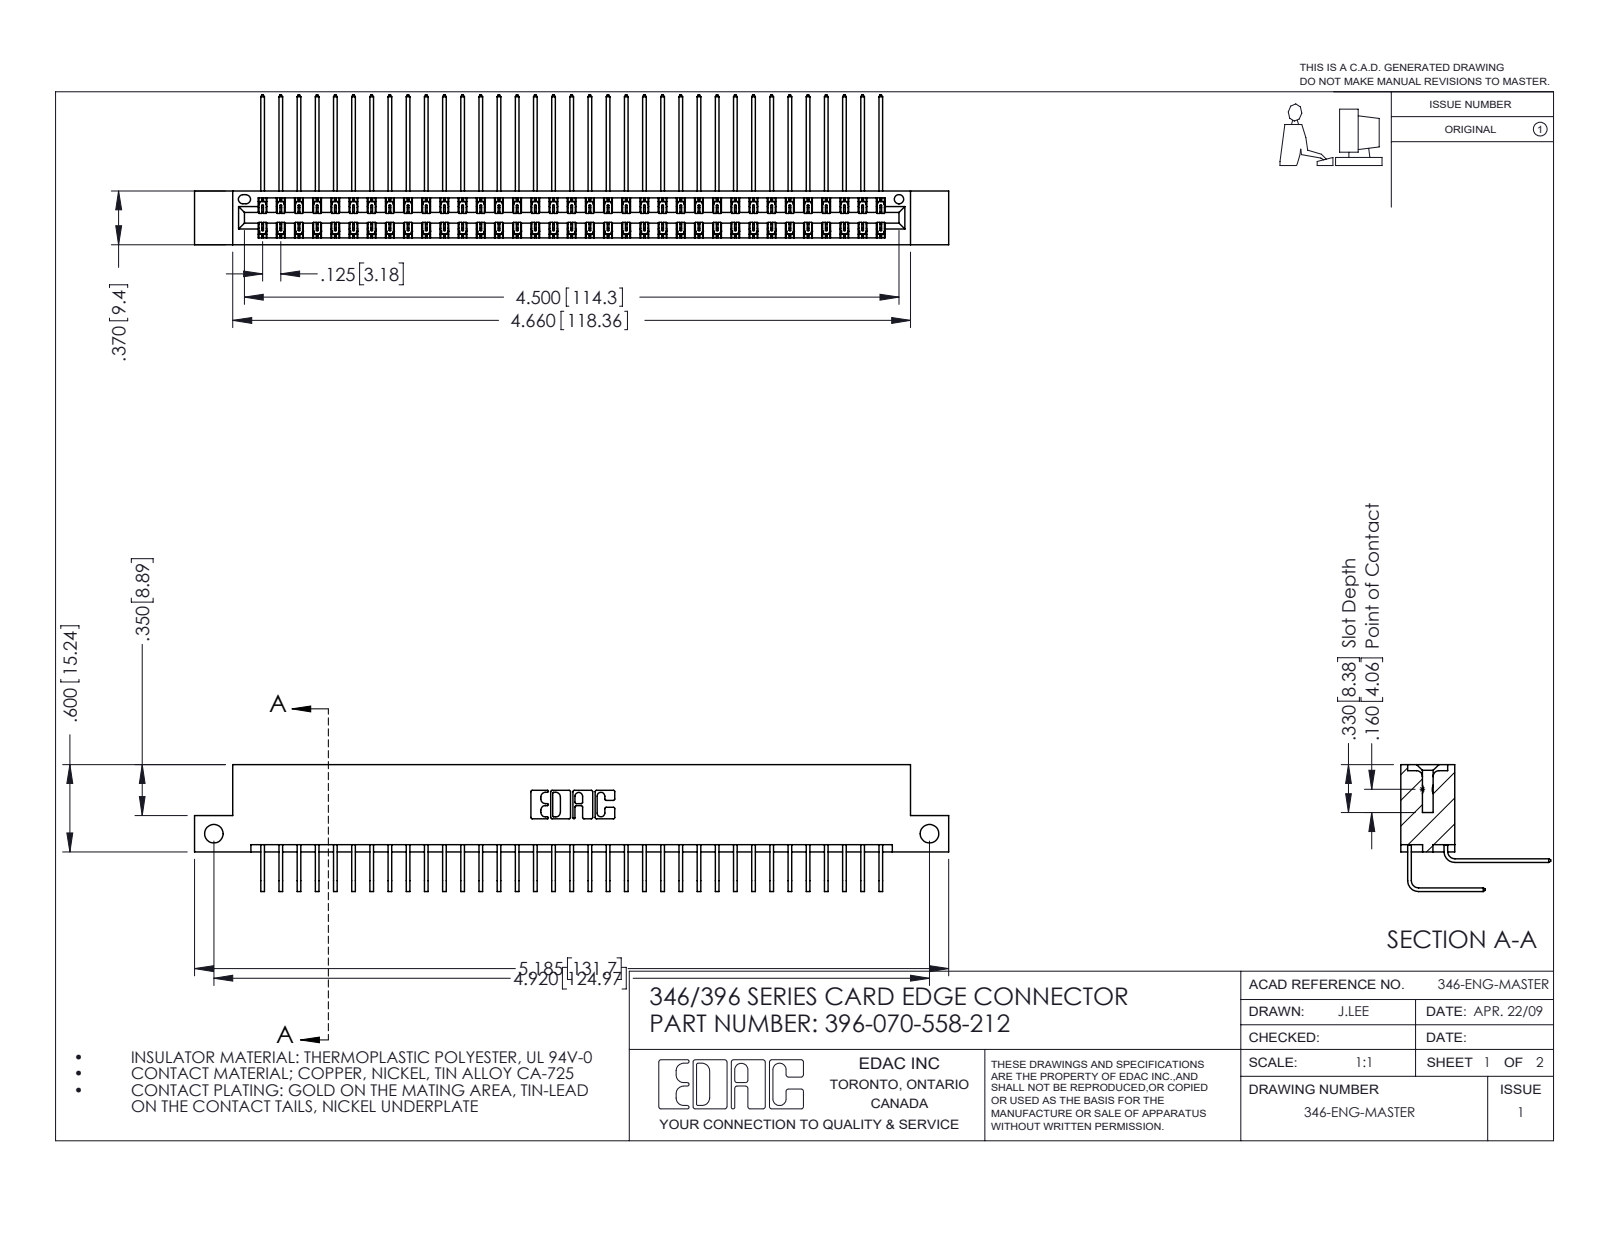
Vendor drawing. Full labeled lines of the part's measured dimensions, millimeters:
Part name (STEP PRODUCT): 396-070-558-212; 345-292-001_558 Tail - 2; 345-292-001_558 559 Tail - 1; 346 Part_Flush Mounting Lugs - Side Mount
STEP written by: SolidWorks 2016 (CONFIG_CONTROL_DESIGN)
Units: millimetres
Bodies: 71 solids, 3902 faces (2666 planar, 1236 cylindrical, 0 other)
Overall size (bounding box): 131.7 × 26.2 × 22.2
Volume: 13 100 mm³ · Surface area: 19 700 mm²
Round holes (diameter × count): ⌀3.3 ×2, ⌀1.6 ×1
Partial cylindrical surfaces — rounded edges, fillets, slot ends (radius × count): R0.2 ×105, R0.3 ×22, R0.2 ×6, R0.8 ×6, R0.7 ×3, R0.4 ×2, R0.6 ×2, R0.6 ×2
Main face-to-face distances: 8.2, 1.2, 0.6, 6.4, 9.4, 7.6, 1.8, 7, 3.8, 5.6
Hole centre spacings: 125
